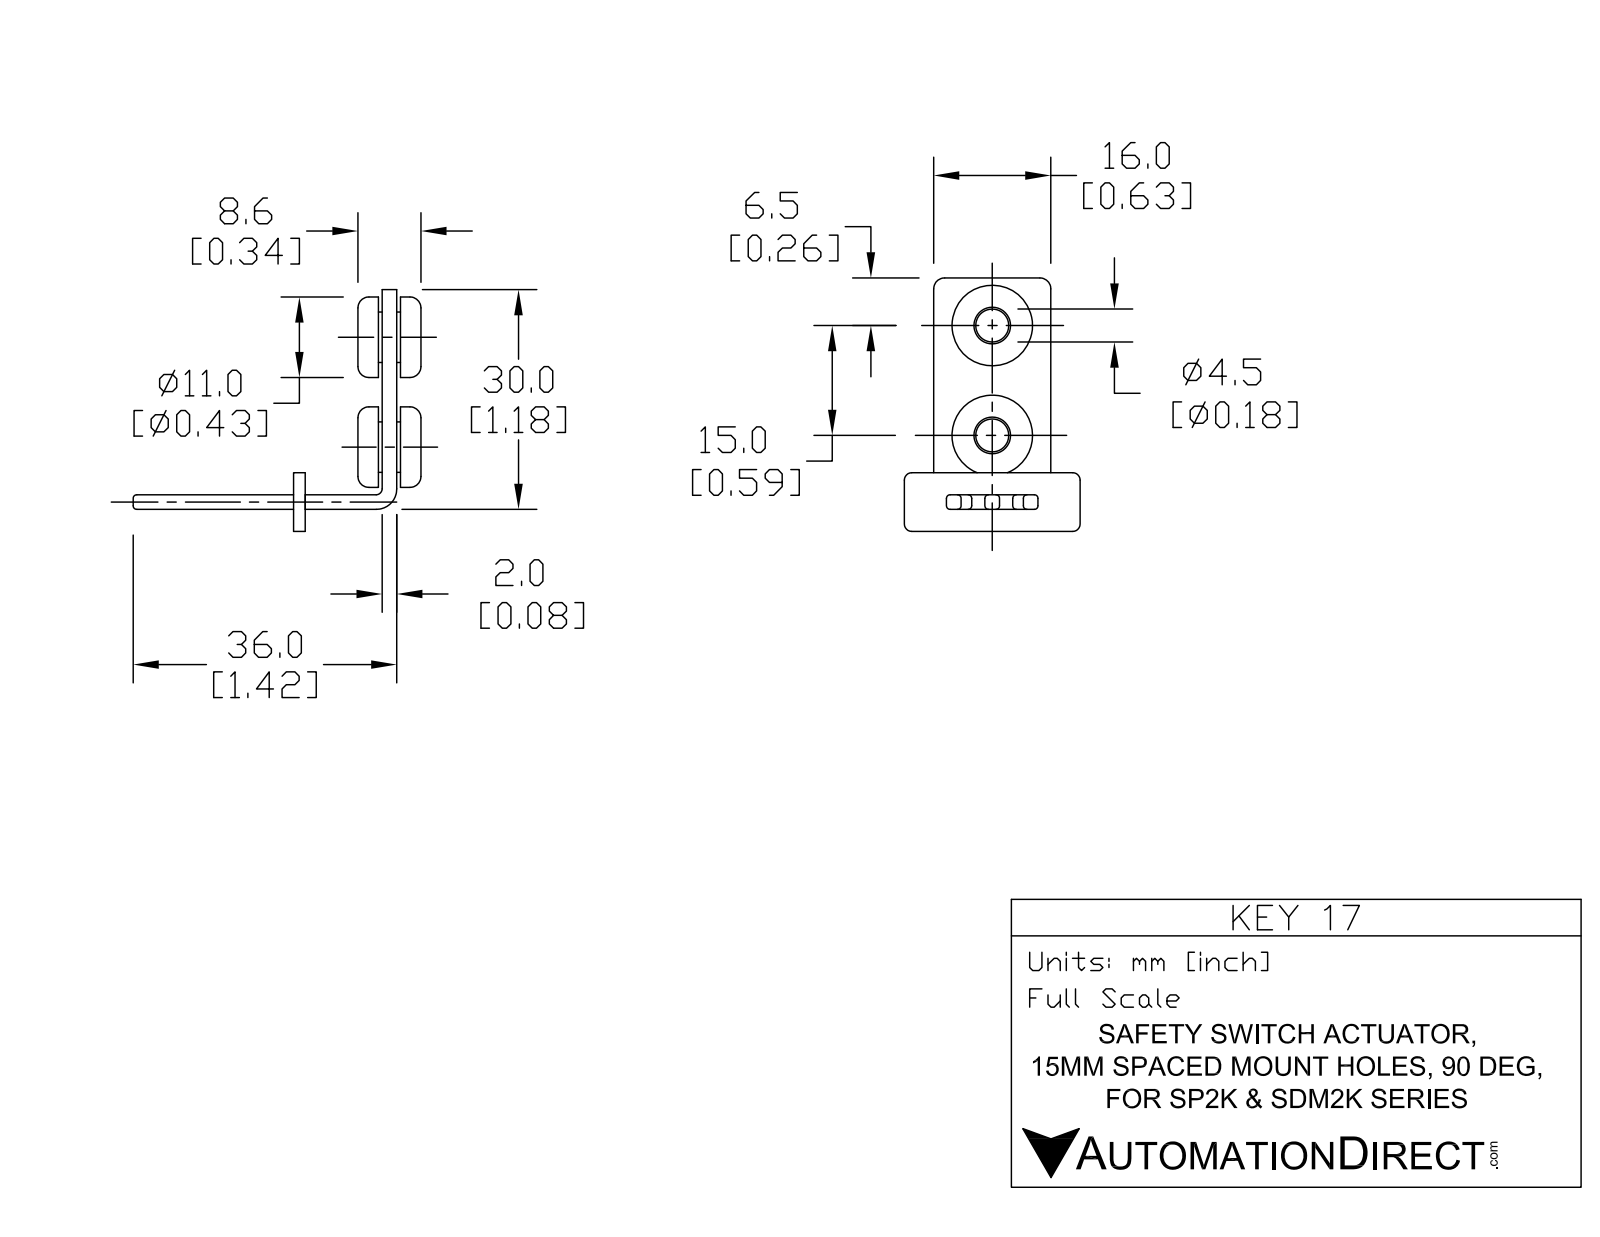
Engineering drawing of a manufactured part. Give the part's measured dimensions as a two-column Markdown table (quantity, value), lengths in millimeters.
| quantity | value |
| --- | --- |
| part name | KEY17 |
| STEP written by | SolidWorks 2019 (CONFIG_CONTROL_DESIGN) |
| units | millimeters |
| bodies | 6 solids, 206 faces (70 planar, 100 cylindrical, 36 other) |
| overall size | 39.1 × 33 × 24 |
| volume | 2 620 mm³ |
| surface area | 4 164 mm² |
| round holes (diameter × count) | 4.5 × 2, 5.5 × 2, 7.1 × 2 |
| round bosses / shafts (diameter × count) | 11 × 2, 6.9 × 2 |
| partial cylindrical surfaces (radius × count) | 0.5 × 42, 1 × 6, 1.5 × 6, 0.2 × 4, 0.8 × 1, 2.8 × 1 |
| main face-to-face distances | 2, 2.5, 0.5, 3, 12.3, 10.3, 13.9, 11.9, 1.6, 9.8 |
| hole center spacings | 15 |
